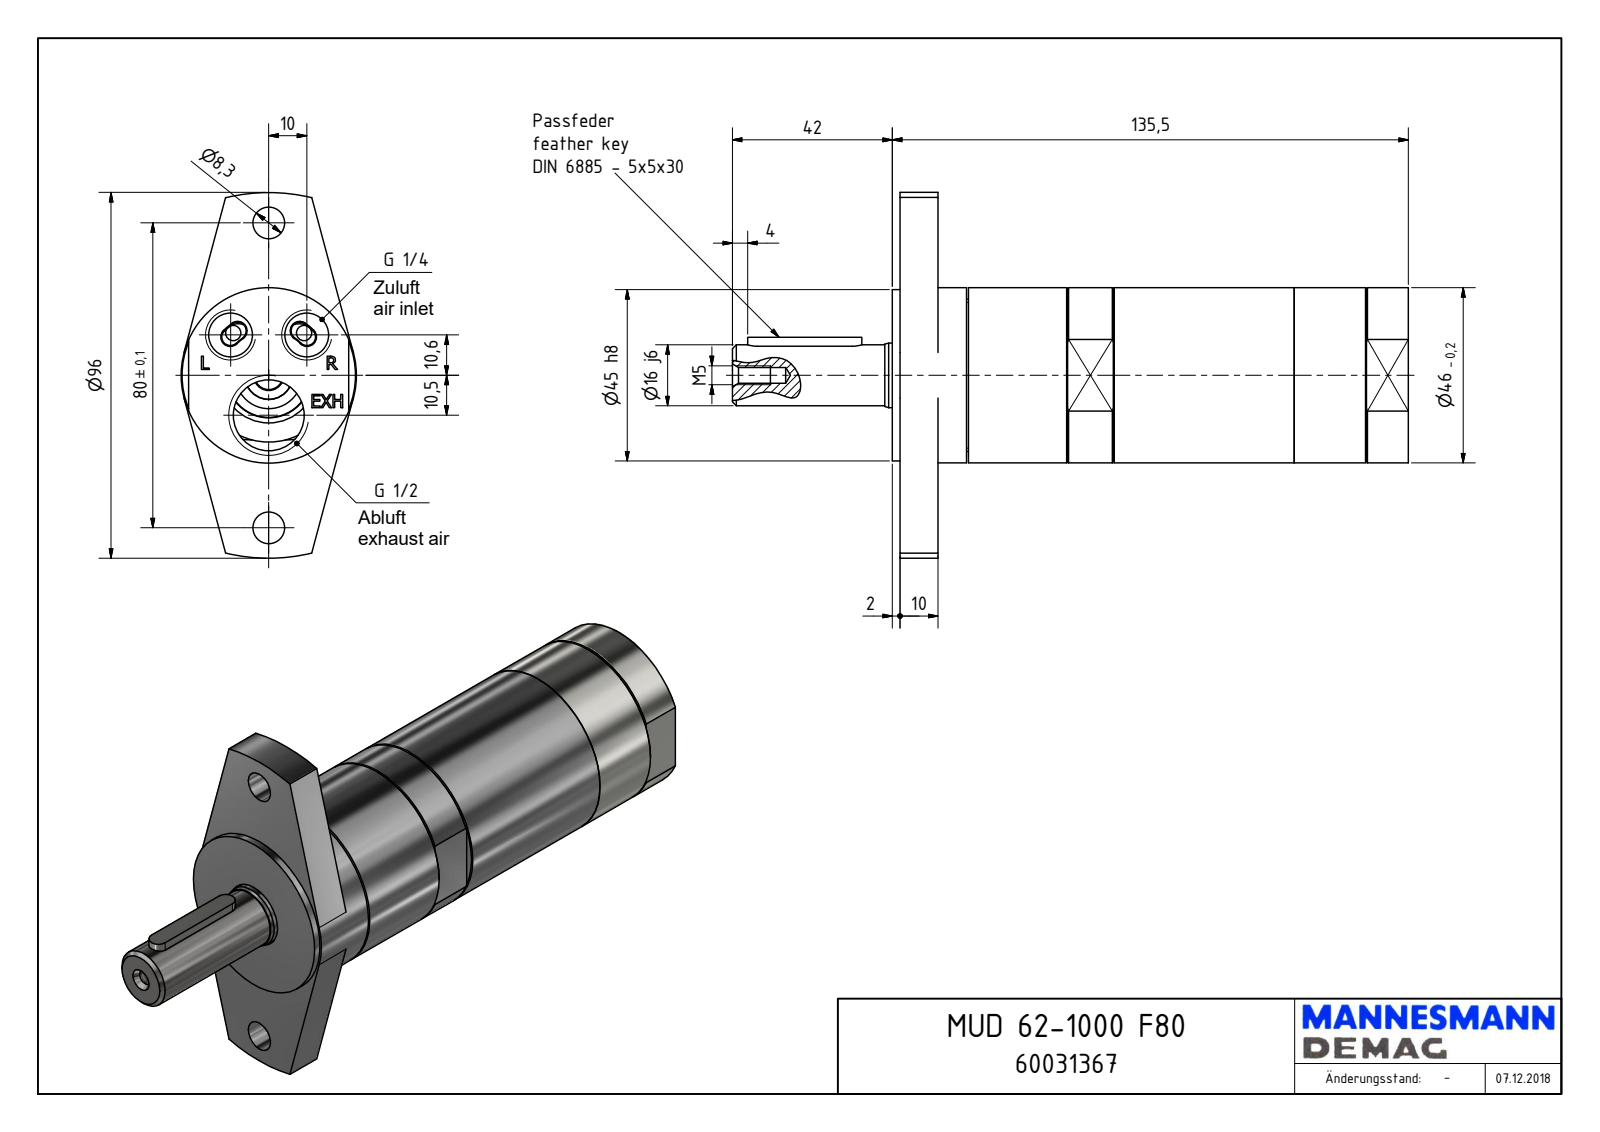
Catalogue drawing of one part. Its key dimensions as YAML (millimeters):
part_name: "MUD 62-1000 F80_60031367"
step_written_by: "Autodesk Inventor 2018 (AUTOMOTIVE_DESIGN)"
units: millimeters
bodies: {solids: 1, faces: 172, planar: 101, cylindrical: 40, other: 31}
overall_size: [177.5, 96, 46]
volume: 242436
surface_area: 34408
round_holes:
  - {diameter: 8.3, count: 2}
  - {diameter: 11.45, count: 2}
  - {diameter: 4.13, count: 1}
  - {diameter: 17.5, count: 1}
  - {diameter: 18.63, count: 1}
  - {diameter: 21.5, count: 1}
  - {diameter: 23, count: 1}
round_bosses_or_shafts:
  - {diameter: 46, count: 1}
  - {diameter: 45, count: 1}
  - {diameter: 40, count: 1}
  - {diameter: 32.6, count: 1}
  - {diameter: 19.56, count: 1}
  - {diameter: 16.95, count: 1}
  - {diameter: 16, count: 1}
partial_cylinders:
  - {radius: 2.5, count: 6}
  - {radius: 5, count: 2}
  - {radius: 16.75, count: 1}
  - {radius: 19, count: 1}
  - {radius: 48, count: 1}
face_to_face_distances: [10, 12, 2, 135.5, 133.5, 123.5, 42, 116.4, 8, 115.5]
hole_center_spacings: [14.57, 23.35, 31.05, 40, 51.58, 10.5, 20, 29.5]
